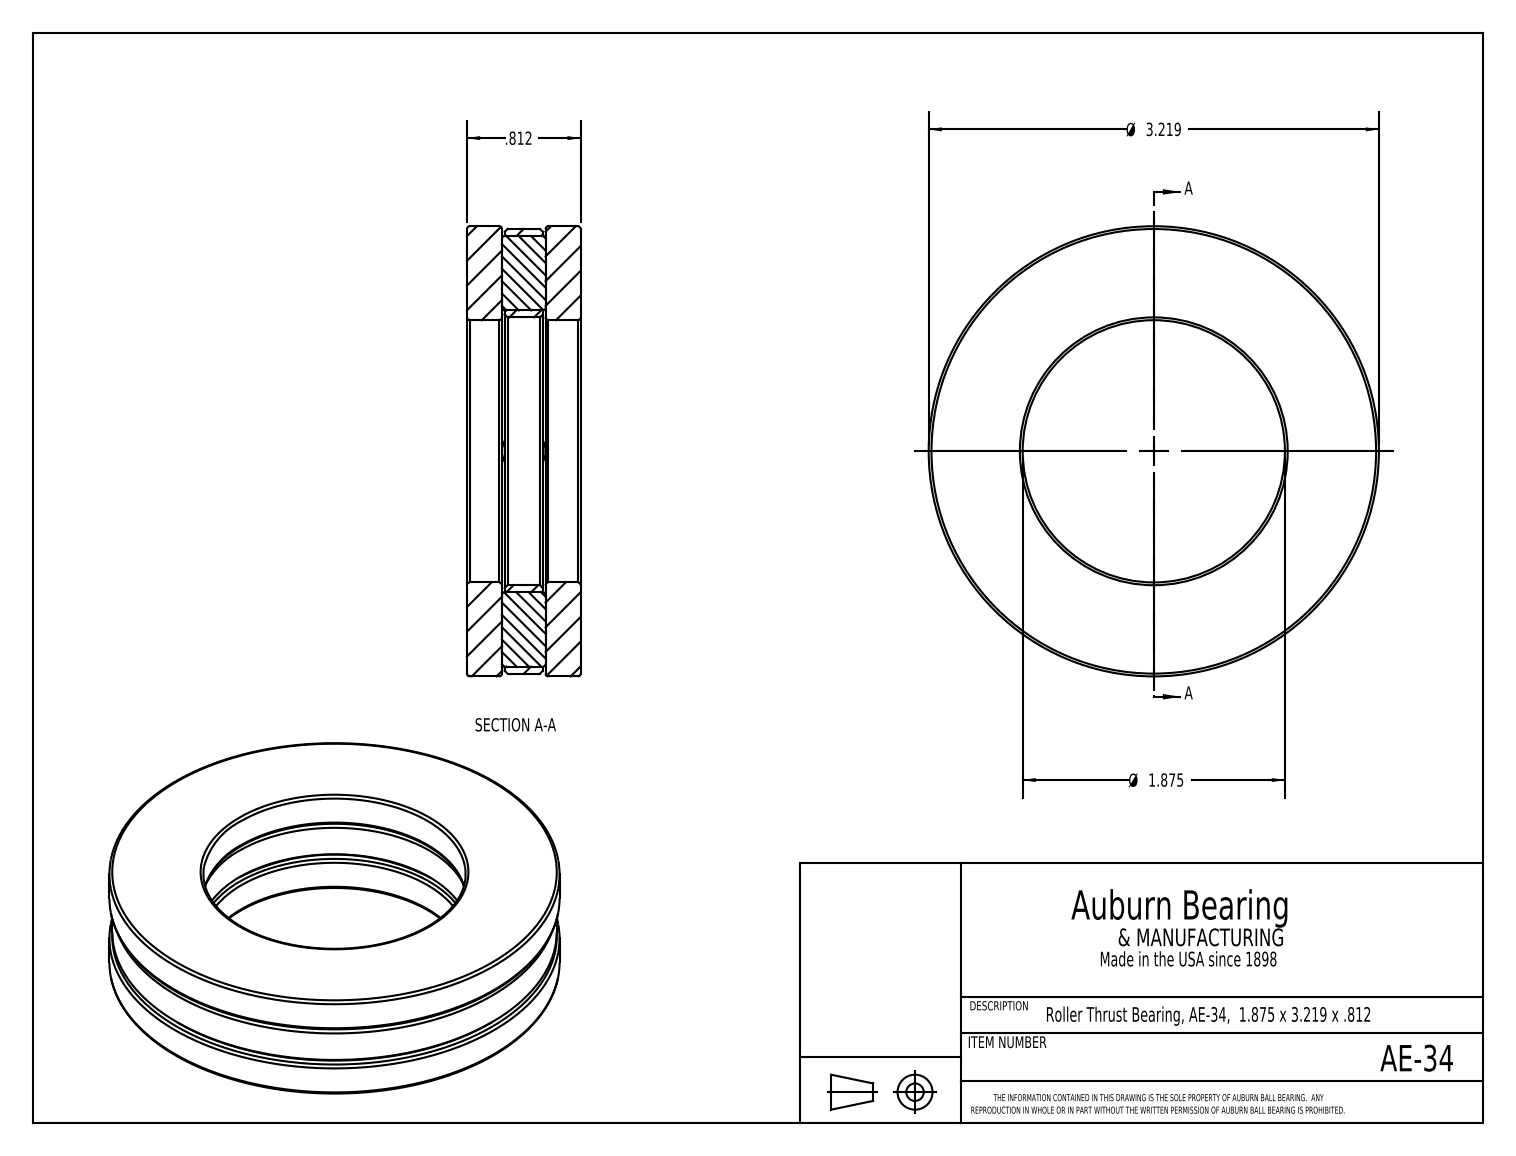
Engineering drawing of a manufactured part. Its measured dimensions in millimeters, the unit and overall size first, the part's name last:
Units: millimetres
Overall size (bounding box): 81.8 × 81.8 × 20.6
Round holes (diameter × count): ⌀47.6 ×1, ⌀48.6 ×1
Round bosses / shafts (diameter × count): ⌀7.9 ×2, ⌀81.8 ×1, ⌀80.7 ×1
Main face-to-face distances: 6.4, 14.3, 6.9, 13.8, 0.5, 7.4, 7.9, 20.6, 6.9, 21.6
Volume: 66 090 mm³ · Surface area: 29 790 mm²
Bodies: 7 solids, 60 faces (30 planar, 10 cylindrical, 20 other)
Part name (STEP PRODUCT): AE-34
STEP written by: SolidWorks 2017 (CONFIG_CONTROL_DESIGN)
